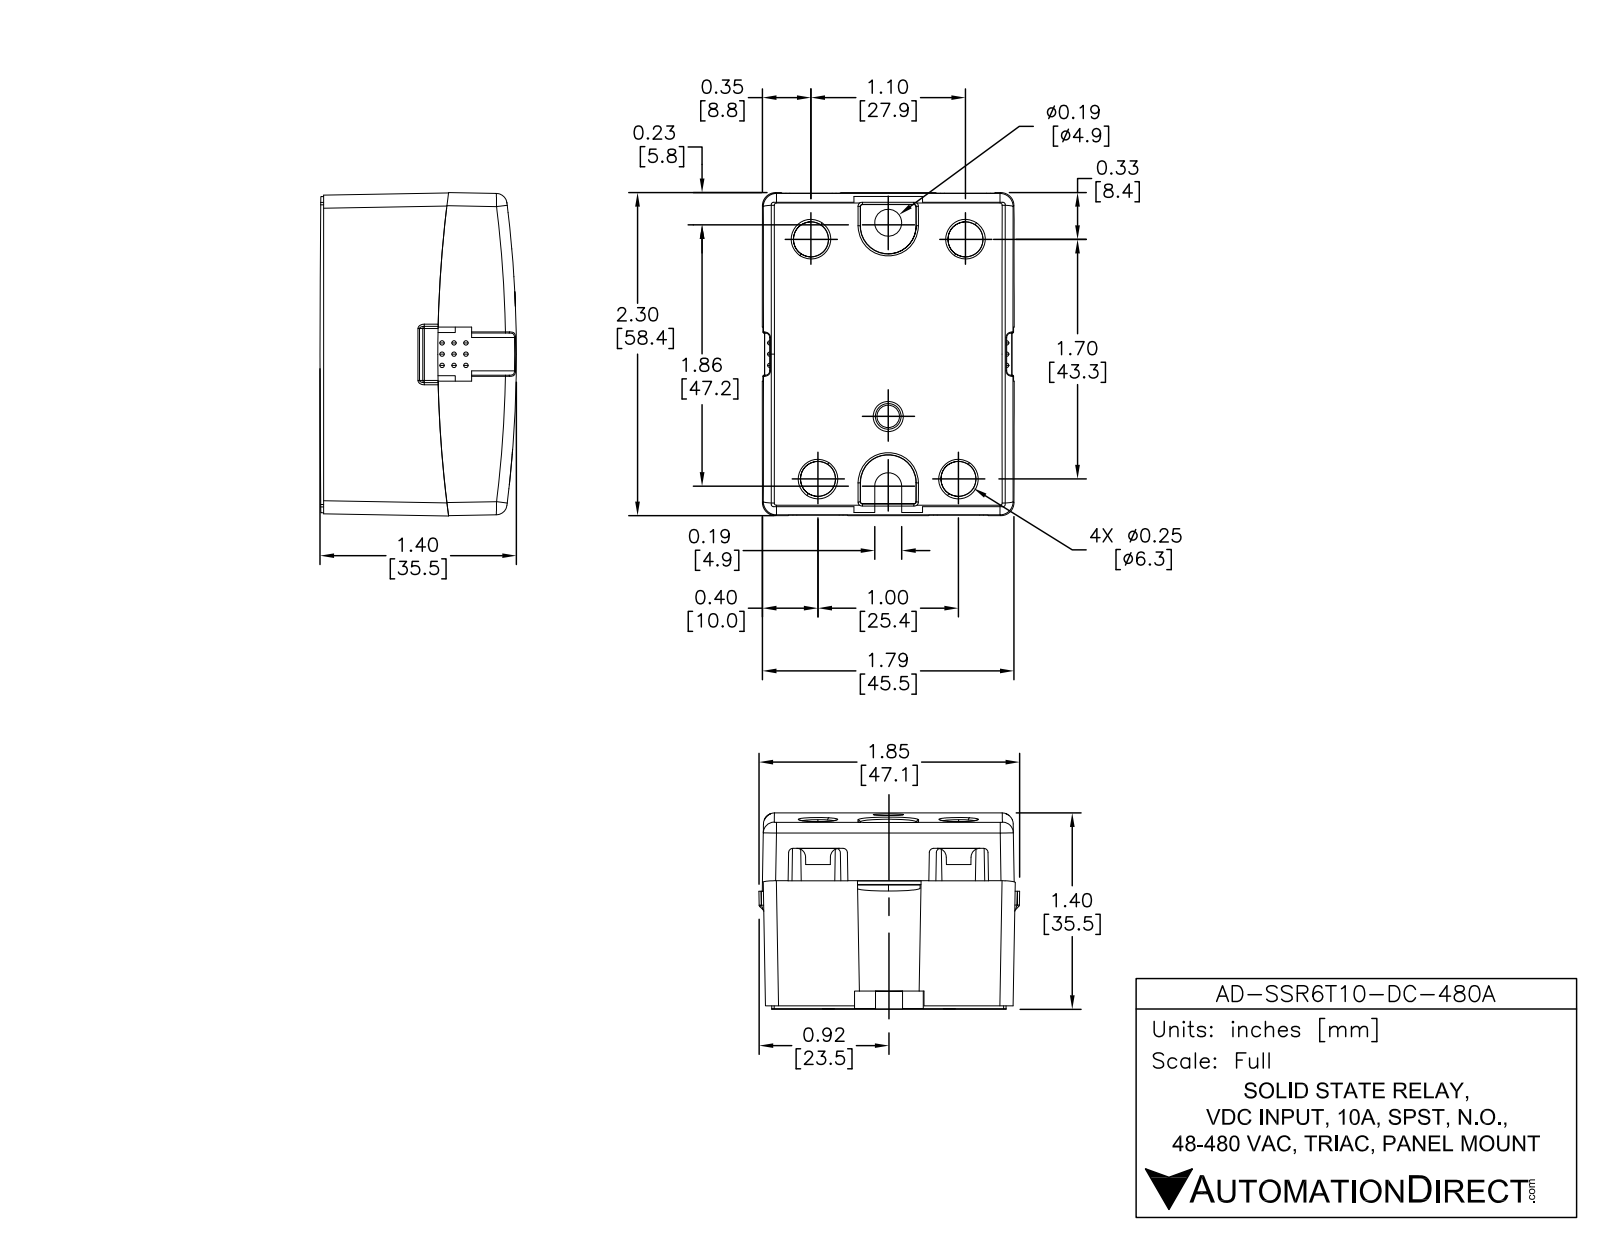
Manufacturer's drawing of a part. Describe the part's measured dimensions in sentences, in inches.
The part is named "AD-SSR6T10-DC-480A". Its 3-D file was written by "SolidWorks 2013 (AUTOMOTIVE_DESIGN)". It is 3 solids with 251 faces: 145 planar, 95 cylindrical and 11 other. Overall it measures 2.3 by 1.79 by 1.4 inches. Its volume is 5.14 cubic inches and its surface area 26.41 square inches. Round holes: 4 of diameter 0.25, 1 of diameter 0.19. Round bosses or shafts: 2 of diameter 0.4, 2 of diameter 0.35, 2 of diameter 0.3, 2 of diameter 0.25, 2 of diameter 0.2, 2 of diameter 0.2. Partial cylindrical surfaces (rounded edges, fillets, slot ends): 6 of radius 0.03, 4 of radius 0.01, 4 of radius 0.04, 4 of radius 0.5, 2 of radius 0.194, 1 of radius 0.095, 1 of radius 0.5, 1 of radius 0.5. The main face-to-face distances are 1.79, 2.3, 1.166, 0.25, 0.916, 0.671, 1.059, 0.5, 1.8, 0.08. The hole center spacings are 0.556, 0.565, 1, 1.1, 1.7, 1.701, 1.876, 1.879.
